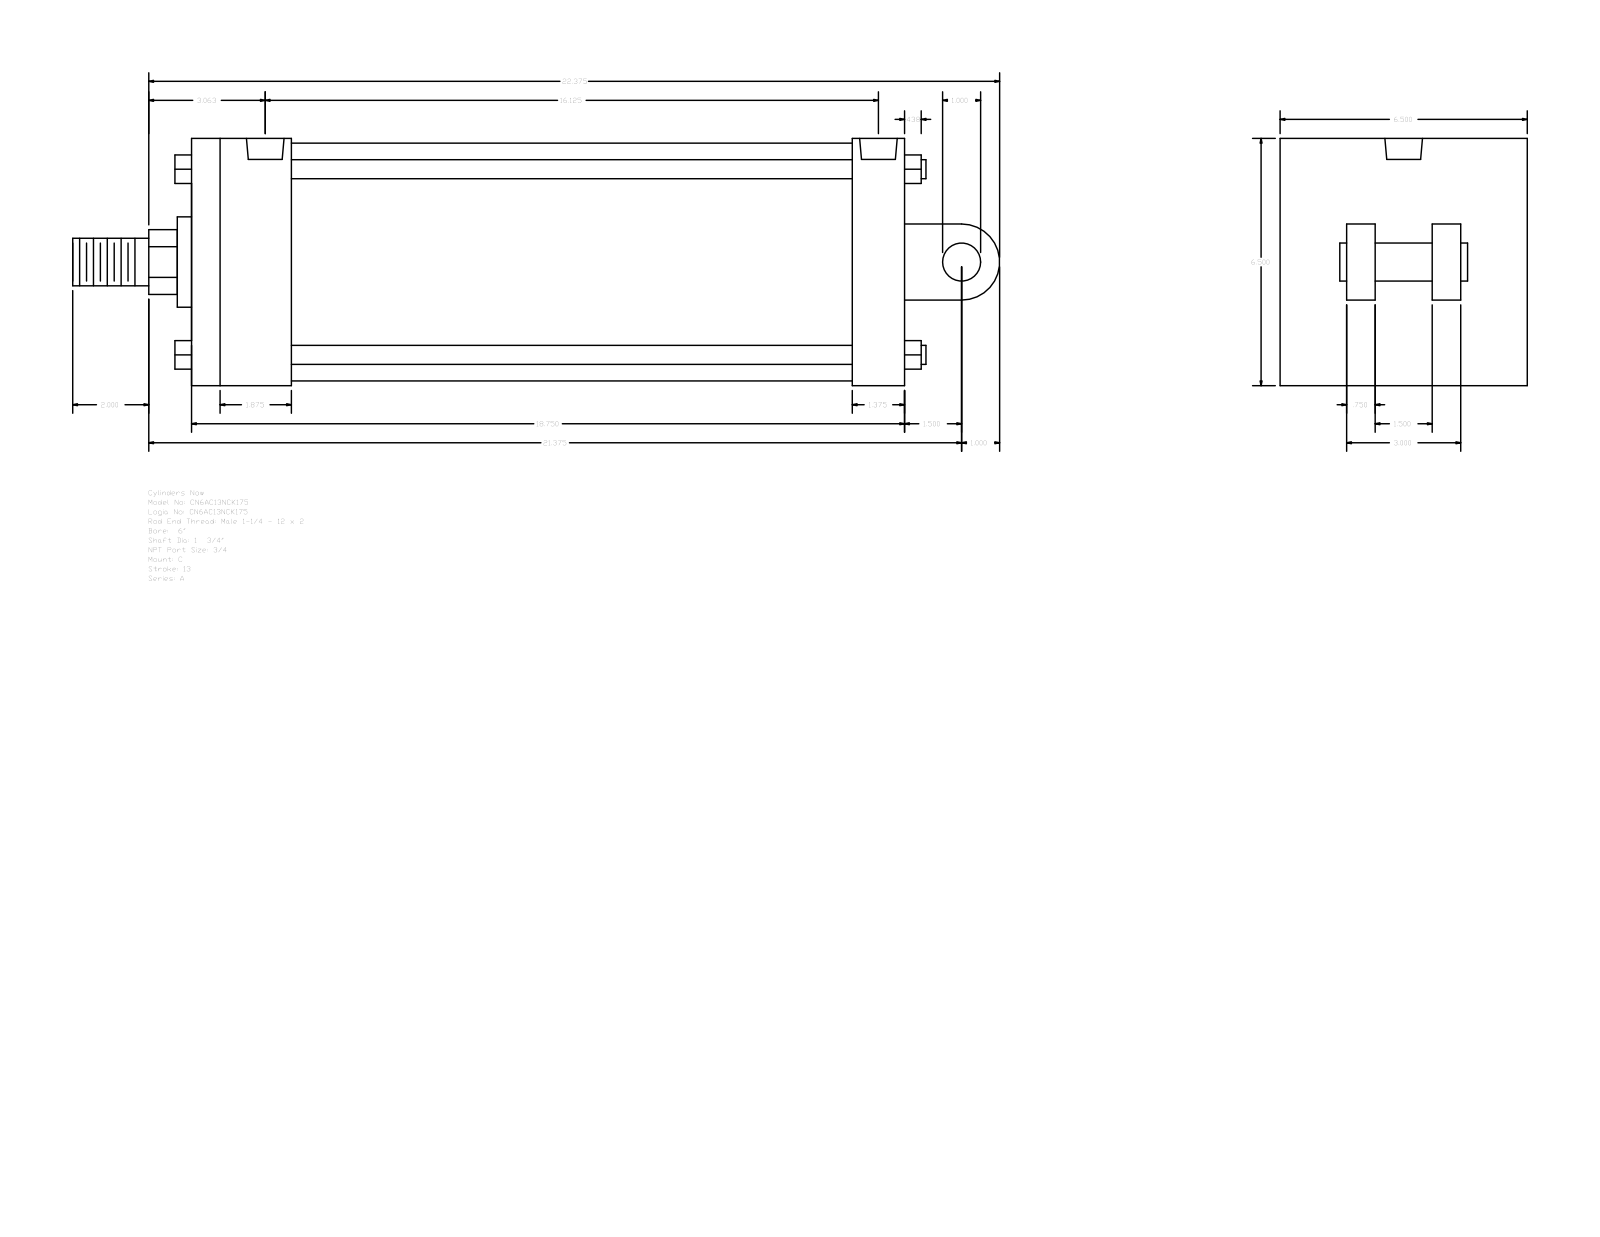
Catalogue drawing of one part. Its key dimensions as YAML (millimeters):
part_name: "A_C__0600_1.75"
step_written_by: "GSSL Pune (CONFIG_CONTROL_DESIGN)"
units: millimeters
bodies: {solids: 0, faces: 135, planar: 102, cylindrical: 33, other: 0}
overall_size: [619.12, 165.1, 165.1]
round_holes:
  - {diameter: 15.08, count: 4}
  - {diameter: 25.12, count: 2}
round_bosses_or_shafts:
  - {diameter: 12.7, count: 4}
  - {diameter: 158.75, count: 1}
  - {diameter: 60.33, count: 1}
  - {diameter: 44.45, count: 1}
  - {diameter: 31.75, count: 1}
  - {diameter: 25.4, count: 1}
partial_cylinders:
  - {radius: 21.63, count: 1}
  - {radius: 25.4, count: 1}
face_to_face_distances: [165.1, 476.25, 19.05, 57.15, 66.68, 409.57, 441.33, 374.65, 34.92, 63.5]
hole_center_spacings: [5.56, 398.45, 404.01, 409.57]
